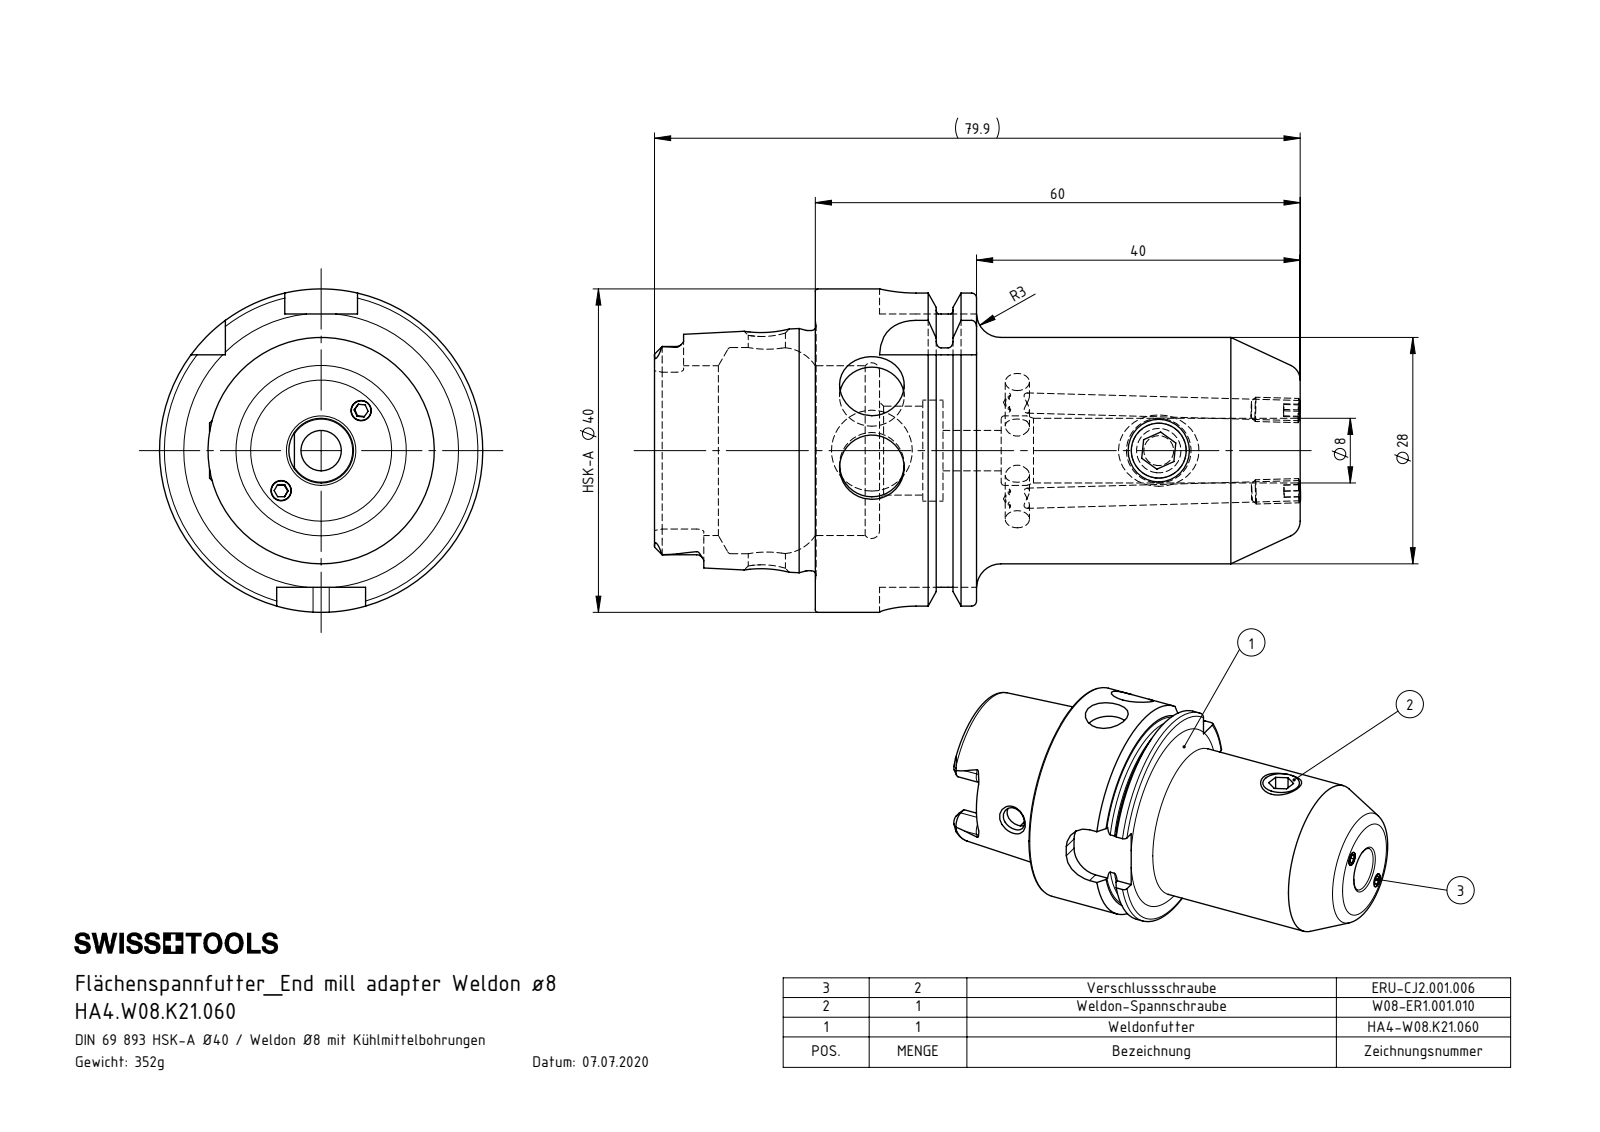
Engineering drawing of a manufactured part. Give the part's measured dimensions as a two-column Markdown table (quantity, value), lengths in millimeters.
| quantity | value |
| --- | --- |
| part name | ERU-CJ2.001.006; HA4-W08.K21.060_A_Fertigbearbeitung; HA4.W08.K21.060; W08-ER1.001.010 |
| STEP written by | SolidWorks 2017 (AUTOMOTIVE_DESIGN) |
| units | millimeters |
| bodies | 4 solids, 190 faces (77 planar, 48 cylindrical, 65 other) |
| overall size | 79.95 × 40 × 40 |
| volume | 44 795 mm³ |
| surface area | 15 131 mm² |
| round holes (diameter × count) | 8 × 3, 2.5 × 2, 3 × 1, 4.6 × 1, 5 × 1, 6.8 × 1, 8.6 × 1, 10 × 1, 11 × 1, 12.5 × 1, 21 × 1, 25.5 × 1 |
| round bosses / shafts (diameter × count) | 3 × 2, 40 × 1, 34.75 × 1, 29.71 × 1, 28 × 1, 8 × 1 |
| partial cylindrical surfaces (radius × count) | 0.9 × 6, 1.88 × 4, 4.5 × 4 |
| main face-to-face distances | 19.95, 7.95, 12, 60, 52.05, 40.05, 19.9, 27.85, 39.85, 79.9 |
| hole center spacings | 35.5 |
